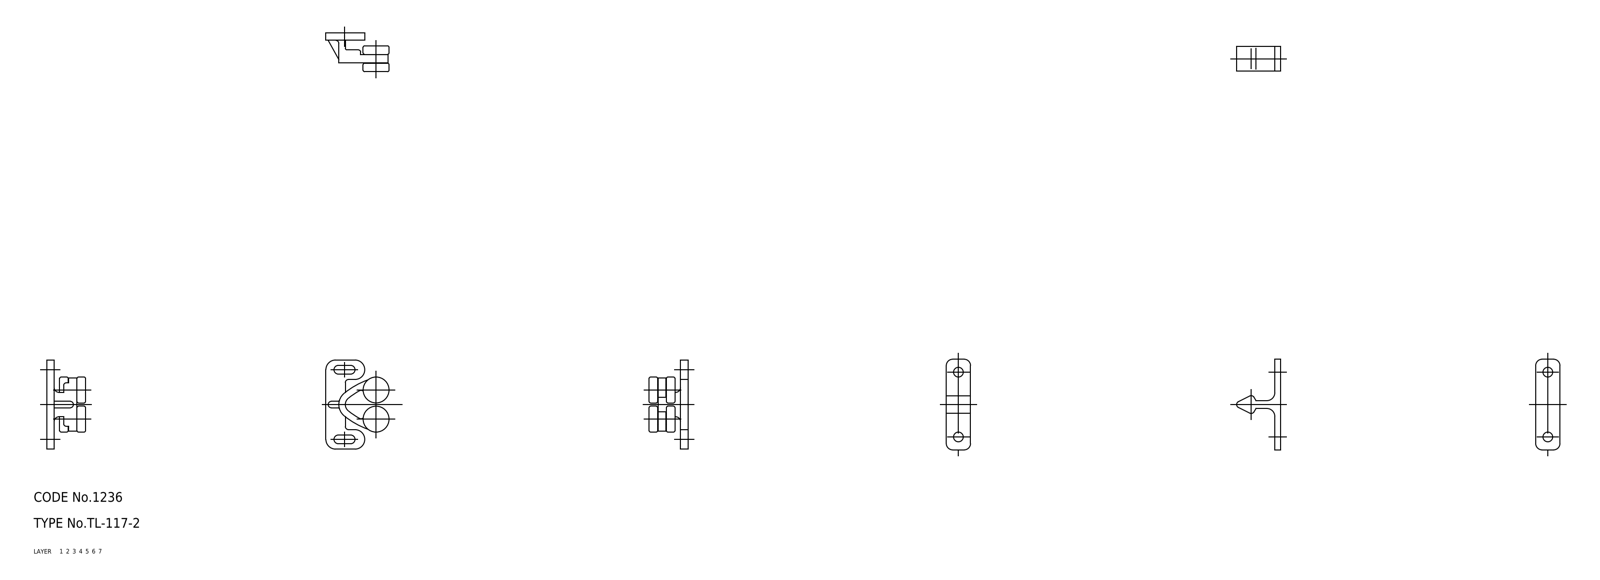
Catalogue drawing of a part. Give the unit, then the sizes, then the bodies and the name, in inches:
Units: inches
Overall size (bounding box): 1.93 × 1.102 × 0.472
Volume: 0.122 in³ · Surface area: 4.095 in²
Bodies: 4 solids, 137 faces (0 planar, 0 cylindrical, 137 other)
Part name (STEP PRODUCT): roller; keeper; base; TL_117_2_28840_36
STEP written by: CADfix (AUTOMOTIVE_DESIGN)
